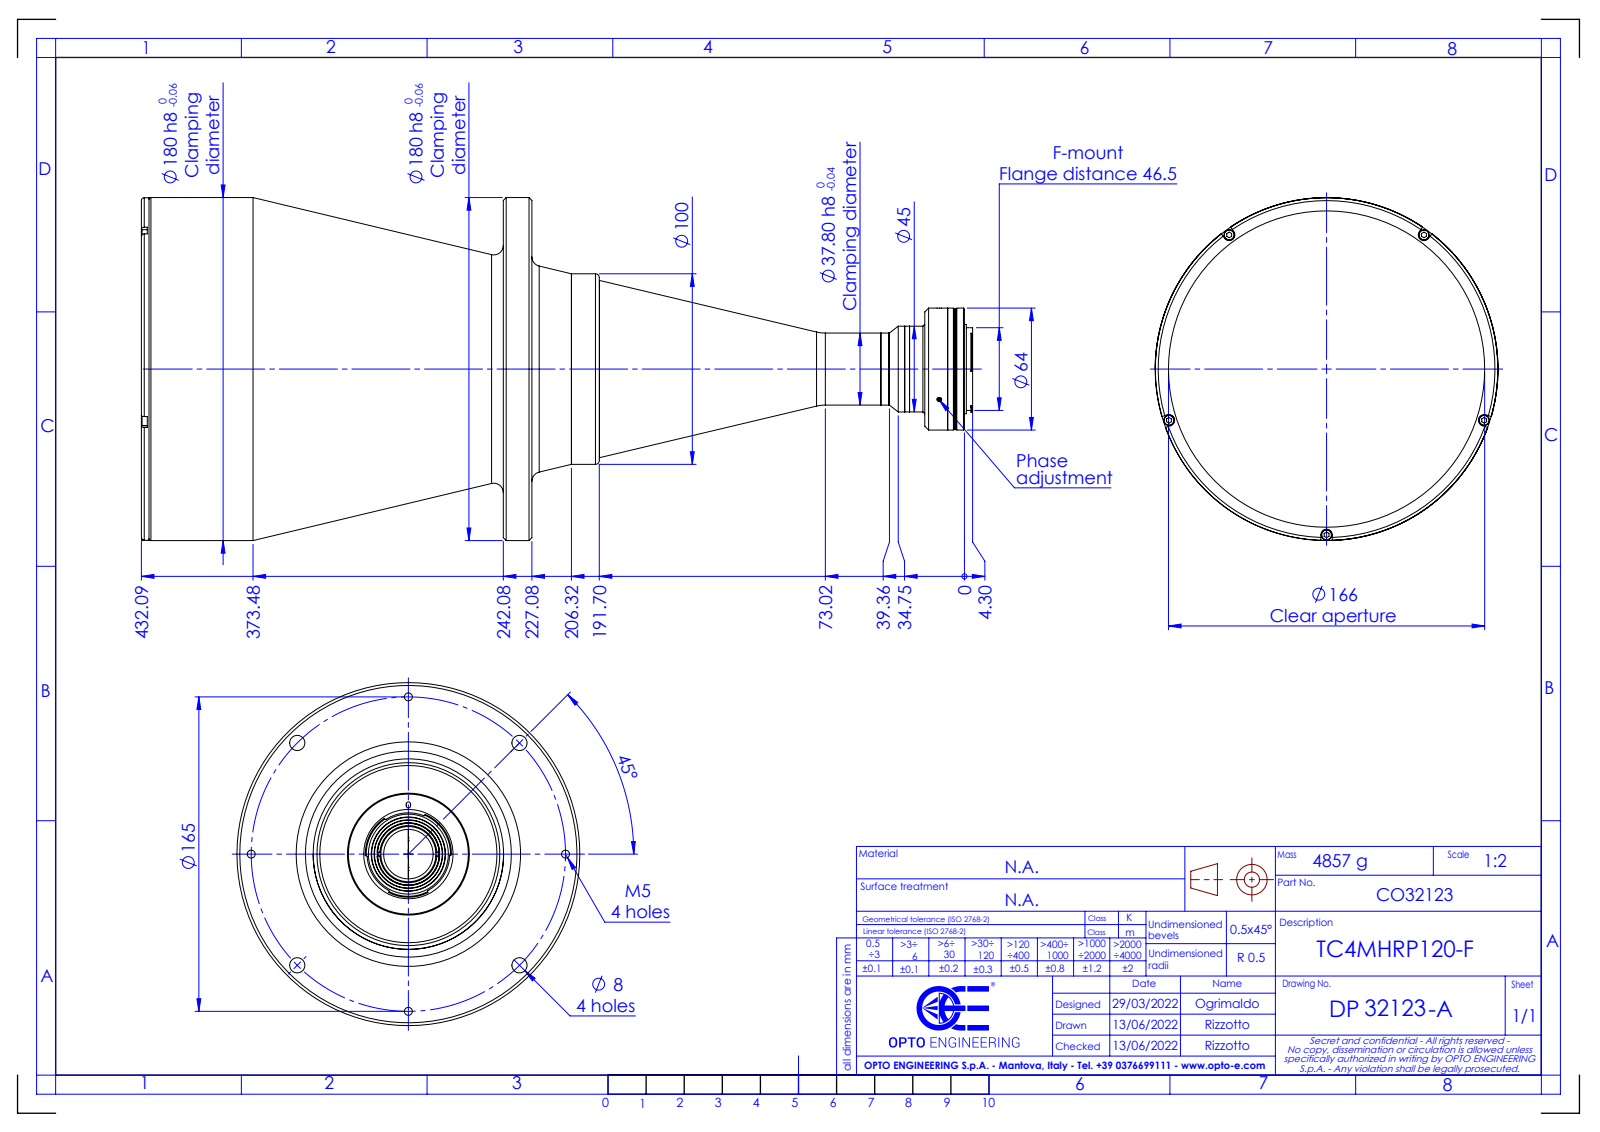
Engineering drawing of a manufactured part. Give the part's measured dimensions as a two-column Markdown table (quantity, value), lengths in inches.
| quantity | value |
| --- | --- |
| part name | DP32123-A_TC4MHRP120-F |
| STEP written by | SolidWorks 2021 (CONFIG_CONTROL_DESIGN) |
| units | inches |
| bodies | 0 solids, 234 faces (72 planar, 95 cylindrical, 67 other) |
| overall size | 17.181 × 7.087 × 7.087 |
| round holes (diameter × count) | 0.165 × 4, 0.315 × 4, 0.098 × 2, 1.142 × 1, 1.654 × 1, 6.535 × 1, 6.724 × 1 |
| round bosses / shafts (diameter × count) | 0.217 × 5, 7.087 × 1, 7.079 × 1, 3.937 × 1, 3.661 × 1, 2.52 × 1, 2.5 × 1, 1.846 × 1 |
| partial cylindrical surfaces (radius × count) | 0.118 × 4, 0.045 × 2, 0.02 × 1, 0.892 × 1 |
| main face-to-face distances | 0.591, 0.157, 7.481, 8.071, 7.323, 7.914, 16.854, 17.011, 9.531, 8.94 |
| hole center spacings | 2.486, 6.002, 3.248, 3.248, 4.593, 4.594, 6.496, 6.496 |
